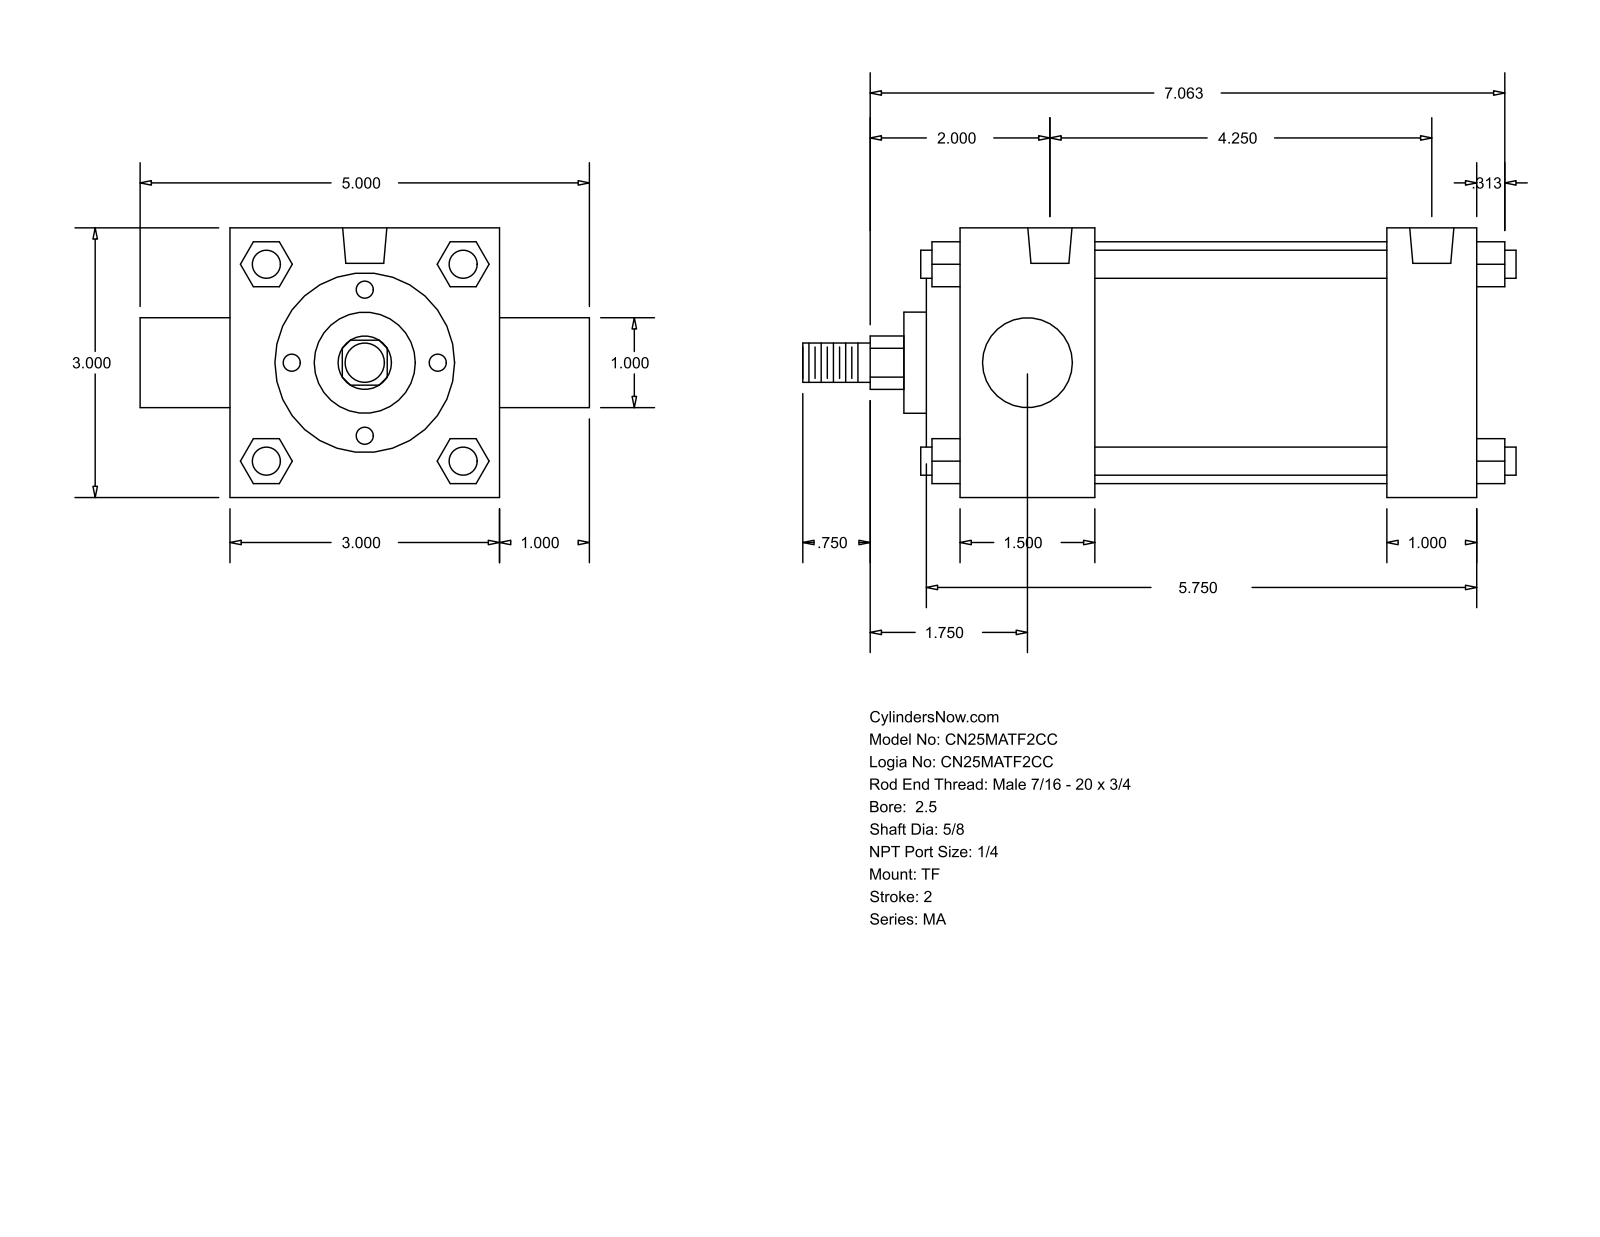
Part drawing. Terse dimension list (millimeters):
name: MA_TF__0250_0.625
written by: GSSL Pune (CONFIG_CONTROL_DESIGN)
unit: mm
bodies: 0 solids, 122 faces (93 planar, 29 cylindrical, 0 other)
size: 201.61 × 127 × 76.2
holes: 3× ⌀7.94, 2× ⌀12.49
bosses: 4× ⌀7.94, 1× ⌀68.33, 1× ⌀50.8, 1× ⌀28.57, 1× ⌀25.4, 1× ⌀15.88, 1× ⌀11.11
rounds: 1× R7.54
face distances: 76.2, 146.05, 25.4, 82.55, 38.1, 120.65, 107.95, 12.7, 9.52, 47.62
hole spacings: 107.95
